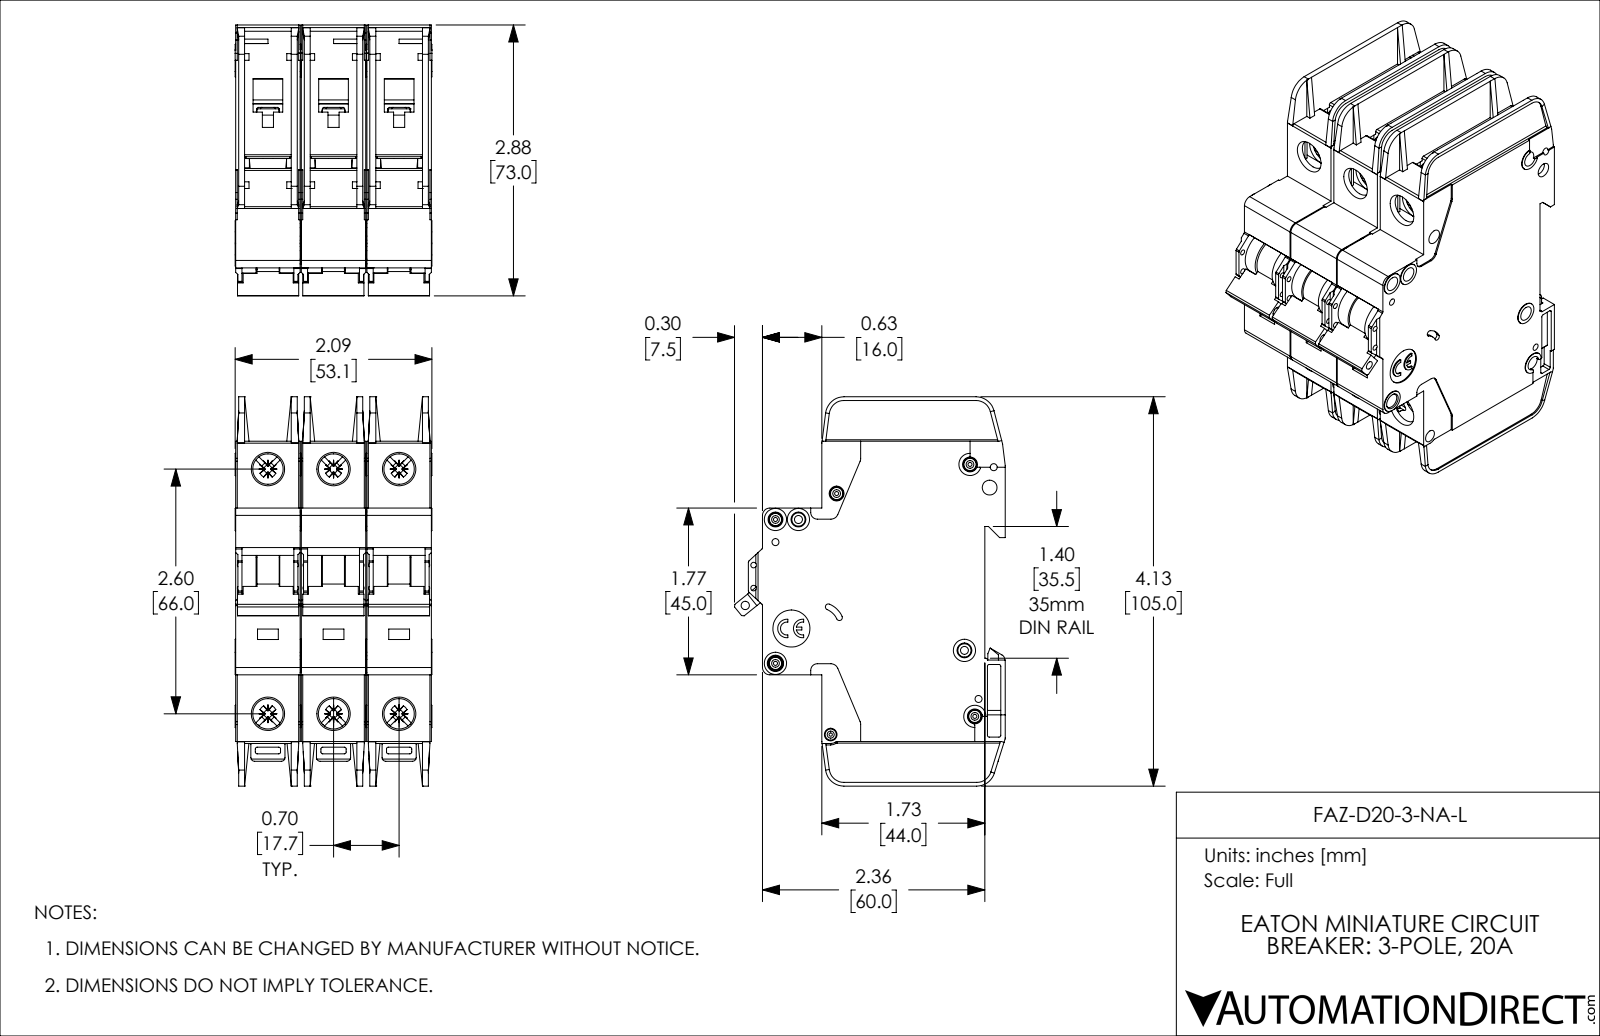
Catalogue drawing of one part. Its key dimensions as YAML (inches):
part_name: "FAZ-D20-3-NA-L"
step_written_by: "SolidWorks 2019 (AUTOMOTIVE_DESIGN)"
units: inches
bodies: {solids: 3, faces: 3381, planar: 2013, cylindrical: 1071, other: 297}
overall_size: [4.134, 2.876, 2.091]
volume: 14.05
surface_area: 123
round_holes:
  - {diameter: 0.157, count: 8}
  - {diameter: 0.323, count: 6}
  - {diameter: 0.043, count: 5}
  - {diameter: 0.075, count: 4}
  - {diameter: 0.059, count: 2}
  - {diameter: 0.085, count: 2}
  - {diameter: 0.035, count: 1}
  - {diameter: 0.089, count: 1}
  - {diameter: 0.098, count: 1}
  - {diameter: 0.134, count: 1}
  - {diameter: 0.394, count: 1}
round_bosses_or_shafts:
  - {diameter: 0.13, count: 5}
  - {diameter: 0.236, count: 4}
  - {diameter: 0.118, count: 4}
  - {diameter: 0.098, count: 3}
partial_cylinders:
  - {radius: 0.02, count: 72}
  - {radius: 0.016, count: 30}
  - {radius: 0.039, count: 18}
  - {radius: 0.043, count: 12}
  - {radius: 0.079, count: 12}
  - {radius: 0.008, count: 6}
  - {radius: 0.01, count: 6}
  - {radius: 0.028, count: 6}
face_to_face_distances: [0.697, 0.047, 1.394, 0.685, 0.591, 1.382, 0.744, 0.65, 0.106, 0.094]
hole_center_spacings: [0.697, 2.69, 2.598, 0.244, 0.537, 0.87, 1.394, 2.948]
